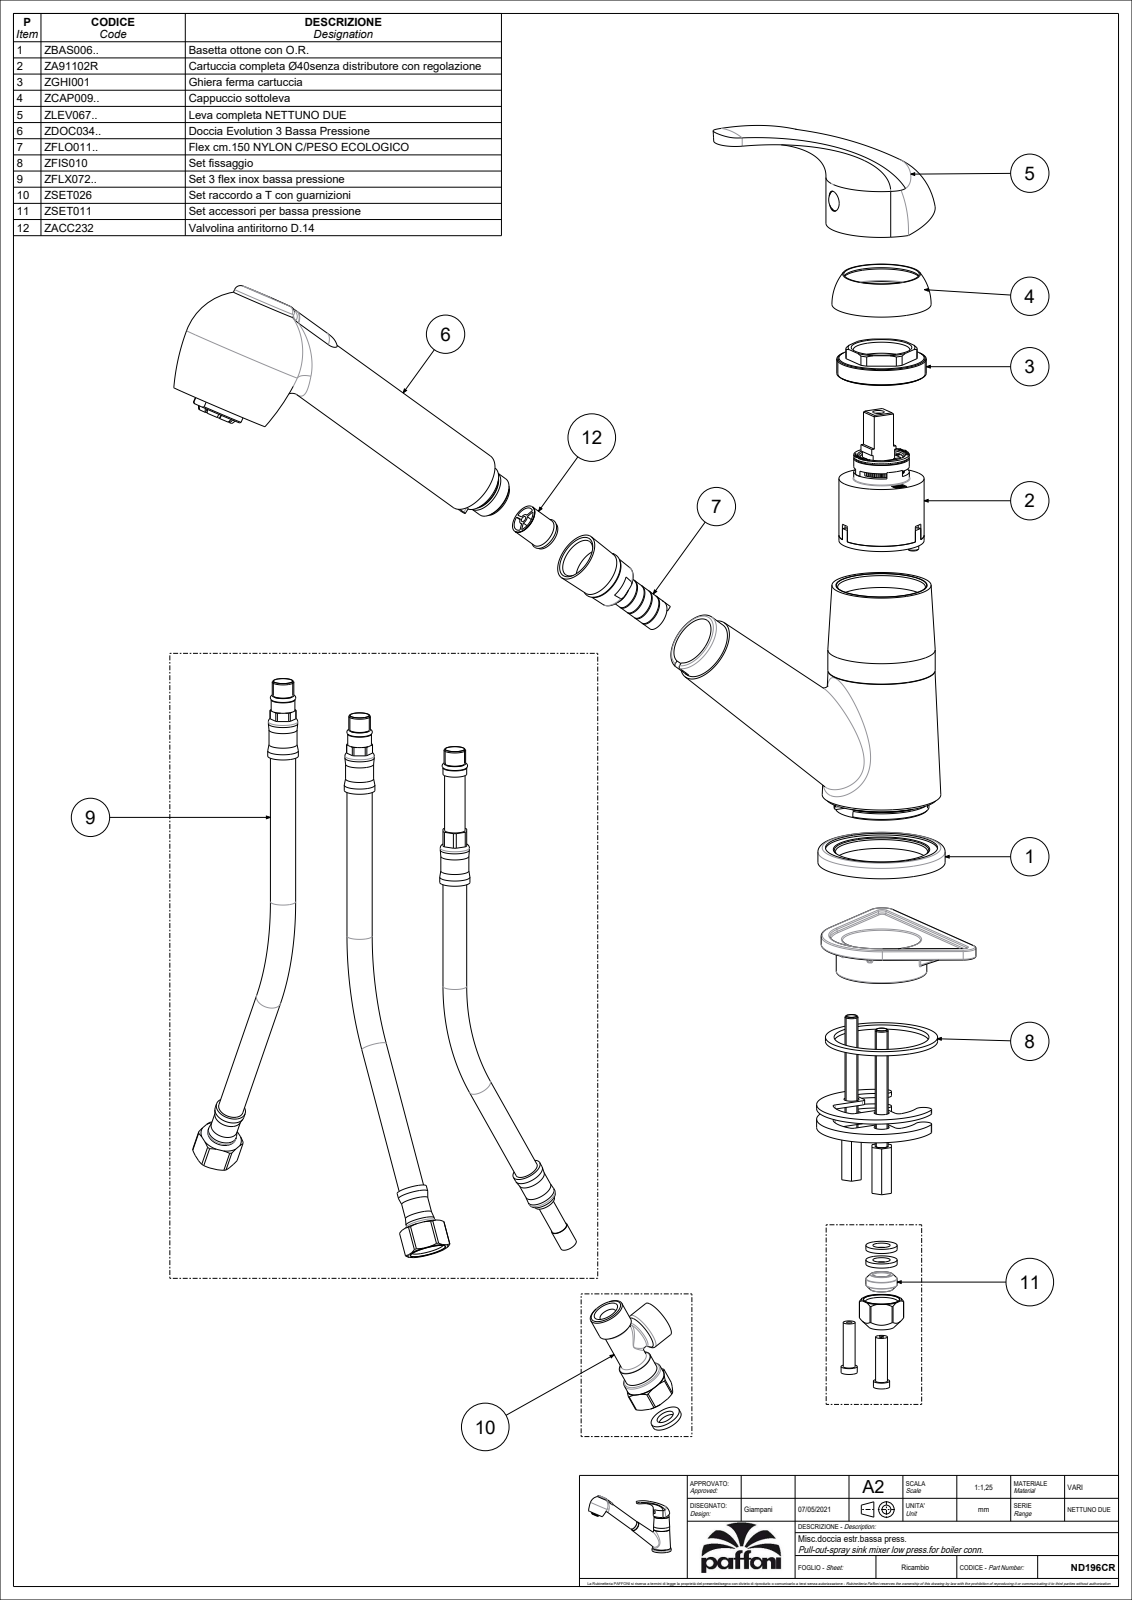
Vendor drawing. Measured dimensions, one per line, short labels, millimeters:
name: ND196CR
written by: CREO PARAMETRIC BY PTC INC, 2020044 (CONFIG_CONTROL_DESIGN)
unit: mm
bodies: 3 solids, 278 faces (103 planar, 67 cylindrical, 108 other)
size: 286.36 × 204.49 × 59
volume: 341 909 mm³; area: 107 469 mm²
holes: 1× ⌀6, 1× ⌀16, 1× ⌀26.2, 1× ⌀35, 1× ⌀40.5, 1× ⌀40.7, 1× ⌀40.9, 1× ⌀42.7, 1× ⌀44, 1× ⌀44.3, 1× ⌀48.2, 1× ⌀49.5
bosses: 2× ⌀5, 1× ⌀59, 1× ⌀49.8, 1× ⌀44.8, 1× ⌀29.5, 1× ⌀28.5, 1× ⌀26, 1× ⌀23
rounds: 2× R8, 1× R2, 1× R3.9, 1× R4, 1× R12, 1× R15, 1× R50
face distances: 122.57, 1, 122.54, 122.6, 67.1, 0.97, 121.57, 121.6, 6.2, 6.17
